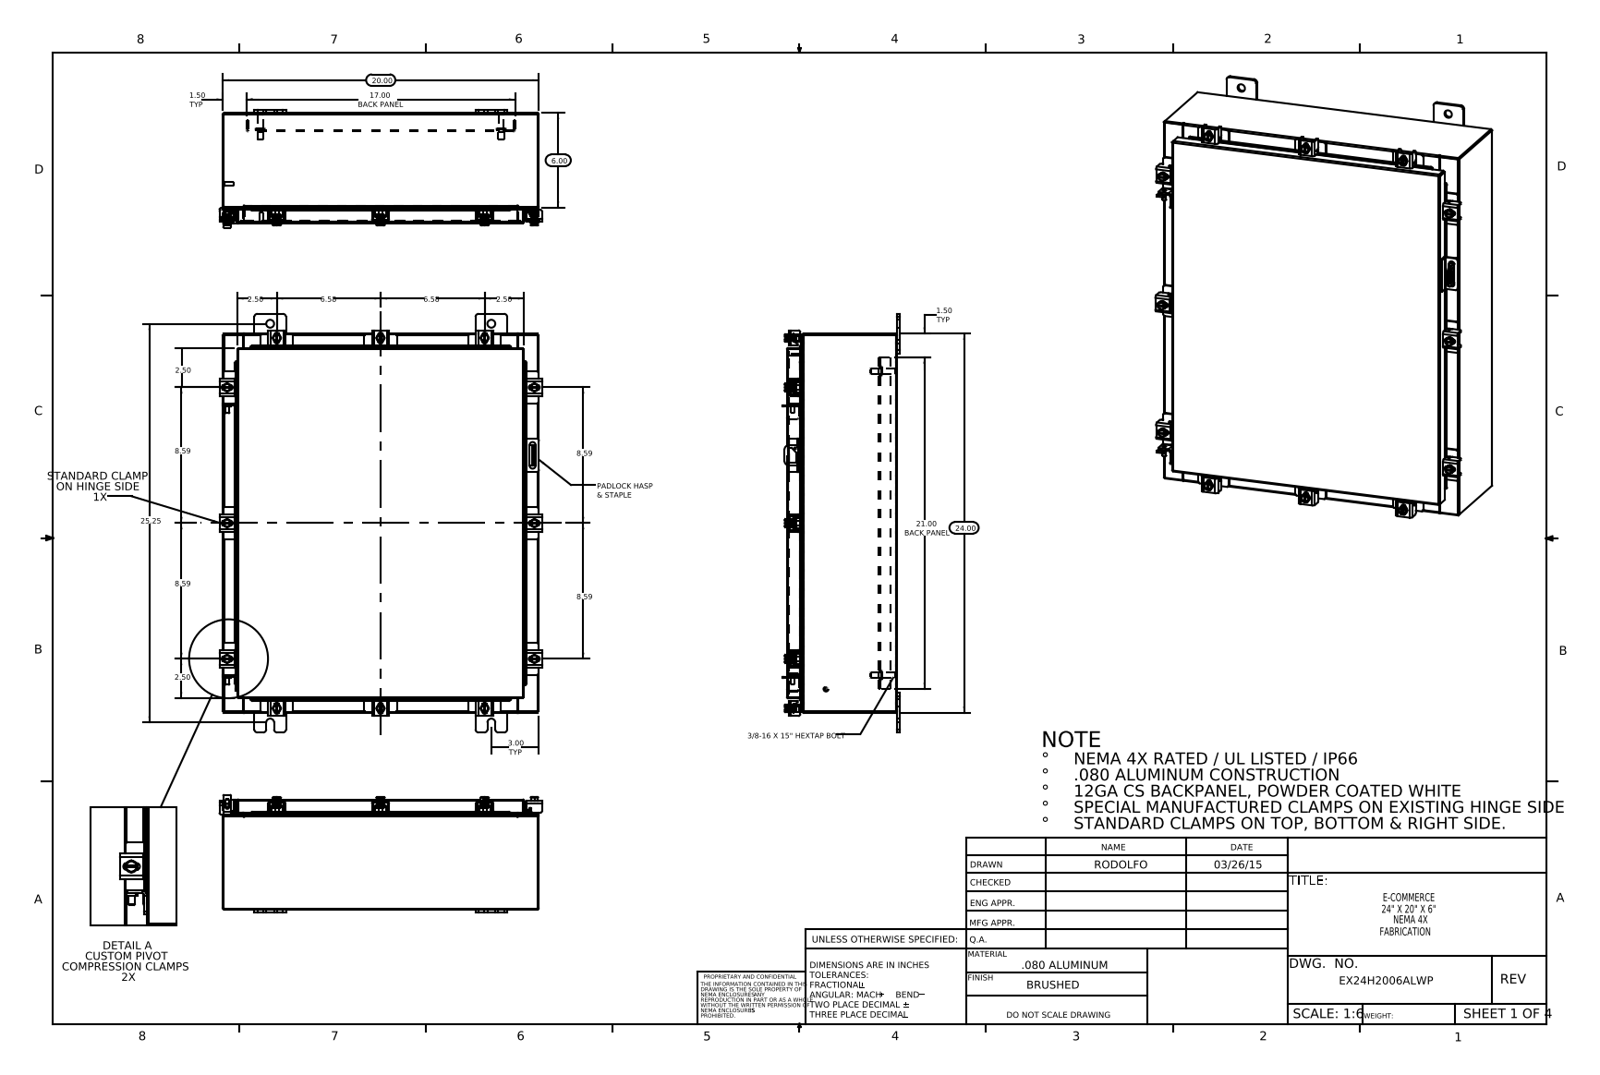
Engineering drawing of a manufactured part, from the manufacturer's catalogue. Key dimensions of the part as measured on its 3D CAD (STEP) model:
Part name (STEP PRODUCT): EX24H2006ALWP Padlock Hasp; Clamp Top_RTP31; Special Clamp Assembly; N-WMT04X30402202210-00 22101002 (+8 more)
STEP written by: SolidWorks 2014 (CONFIG_CONTROL_DESIGN)
Units: inches
Bodies: 81 solids, 2018 faces (1075 planar, 783 cylindrical, 160 other)
Overall size (bounding box): 26.5 × 20.421 × 7.453
Volume: 174.1 in³ · Surface area: 4 334 in²
Round holes (diameter × count): ⌀0.213 ×12, ⌀0.26 ×12, ⌀0.5 ×8, ⌀0.125 ×1, ⌀0.25 ×1
Round bosses / shafts (diameter × count): ⌀0.5 ×12, ⌀0.25 ×12, ⌀0.399 ×10, ⌀0.625 ×4, ⌀0.375 ×4, ⌀0.33 ×4, ⌀0.315 ×2, ⌀0.236 ×2
Partial cylindrical surfaces — rounded edges, fillets, slot ends (radius × count): R0.06 ×54, R0.013 ×24, R0.141 ×24, R0.19 ×24, R0.088 ×22, R0.12 ×22, R0.09 ×18, R0.05 ×17
Main face-to-face distances: 0.075, 6.9, 6.975, 6.826, 0.104, 1, 1.075, 5.826, 5.9, 1.179
Hole centre spacings: 2.347, 4.44, 8.594, 12.141, 16.602, 18.34, 20.082, 20.562
